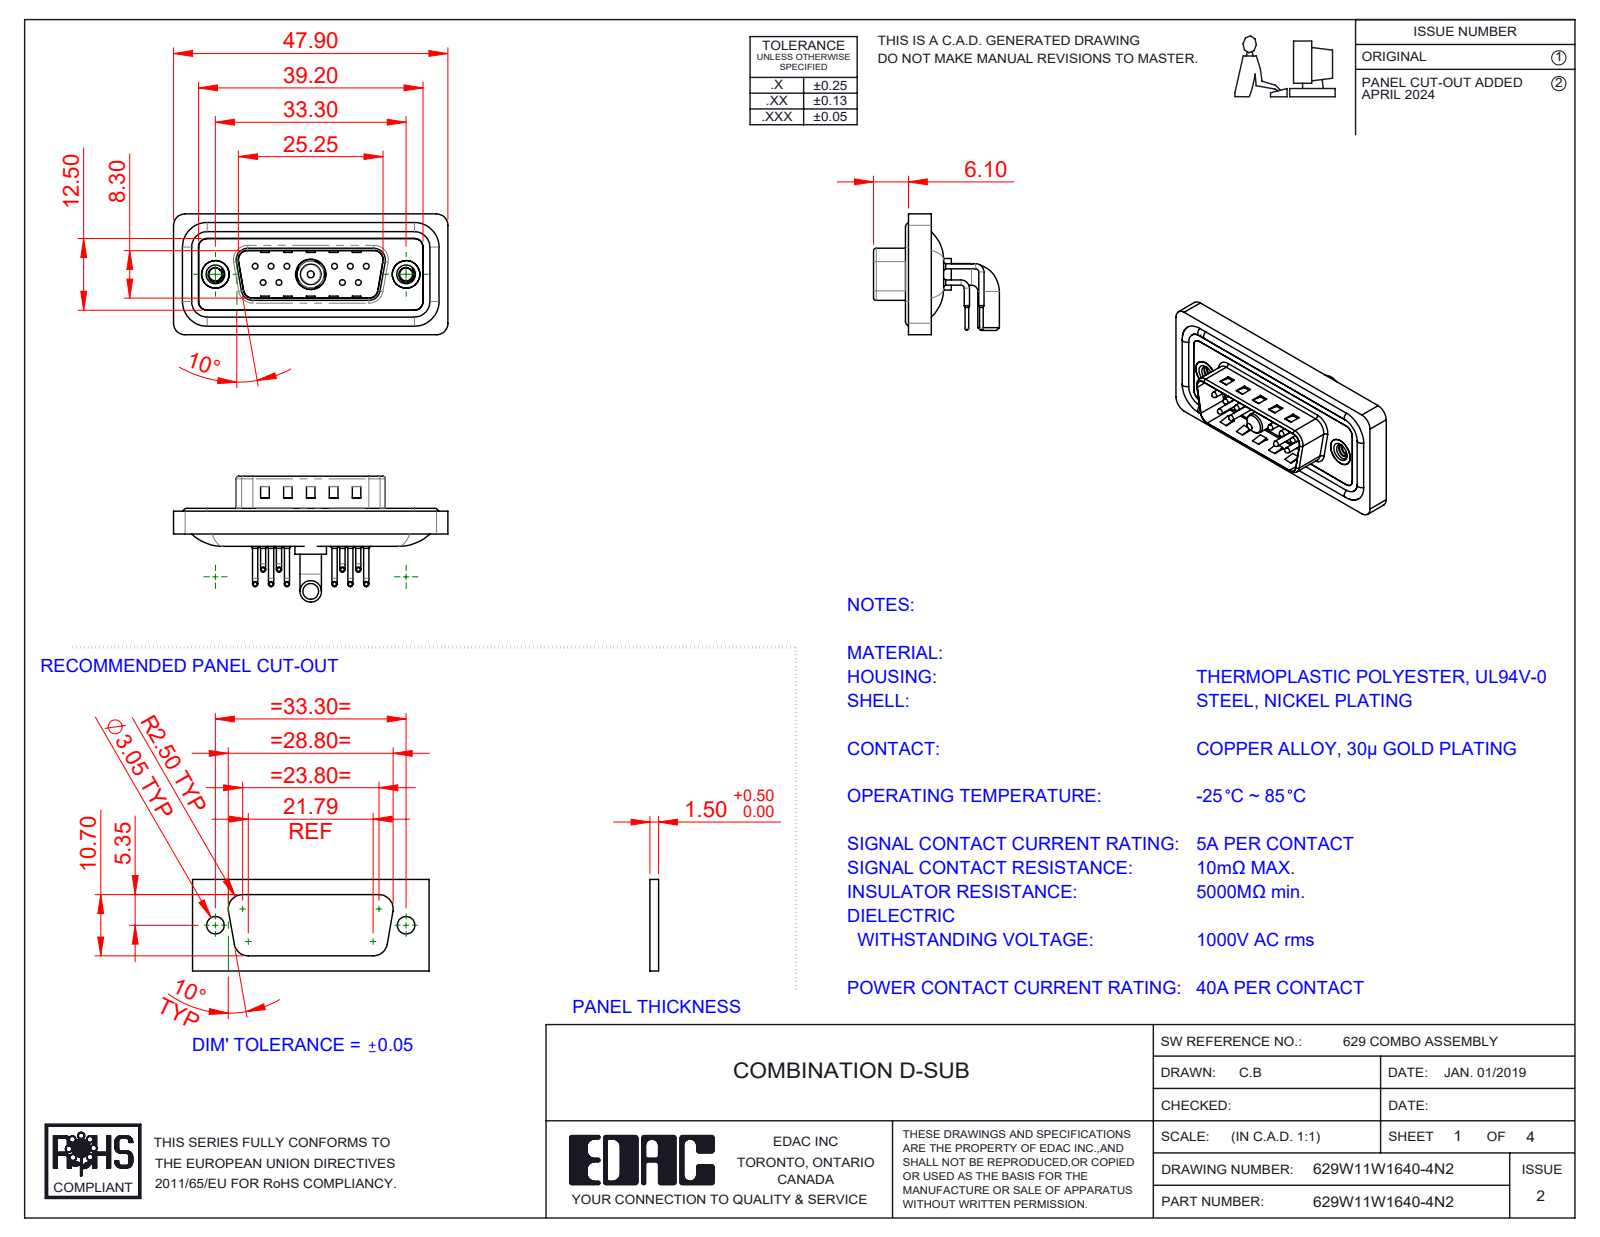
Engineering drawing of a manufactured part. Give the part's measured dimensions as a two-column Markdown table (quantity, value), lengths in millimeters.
| quantity | value |
| --- | --- |
| part name | 629Combo Shell Front_15 Contacts; 629Combo Contact Row 2; 629W11W1640-4N2; 629Combo Shell Rear_15 Contacts (+5 more) |
| STEP written by | SolidWorks 2023 (CONFIG_CONTROL_DESIGN) |
| units | millimeters |
| bodies | 19 solids, 1603 faces (836 planar, 569 cylindrical, 198 other) |
| overall size | 47.9 × 21.98 × 21.1 |
| volume | 5 673 mm³ |
| surface area | 9 324 mm² |
| round holes (diameter × count) | 0.75 × 10, 1.6 × 10, 2 × 10, 2.26 × 2, 4 × 2, 4.8 × 2, 5 × 2, 4.85 × 1, 5.3 × 1 |
| round bosses / shafts (diameter × count) | 0.9 × 20, 1.5 × 10, 1 × 10, 0.65 × 10, 1.6 × 4, 4.9 × 2, 3.75 × 2, 5.5 × 1 |
| partial cylindrical surfaces (radius × count) | 2 × 20, 1.5 × 18, 1.01 × 10, 0.5 × 8, 1.6 × 8, 1 × 7, 0.25 × 4, 0.6 × 4 |
| main face-to-face distances | 0.4, 2.9, 0.8, 1.1, 2.1, 1.6, 2.5, 4.1, 4.5, 3.1 |
| hole center spacings | 3.16, 2.77, 13.85, 11.08, 16.62, 5.03, 5.04, 5.54 |
